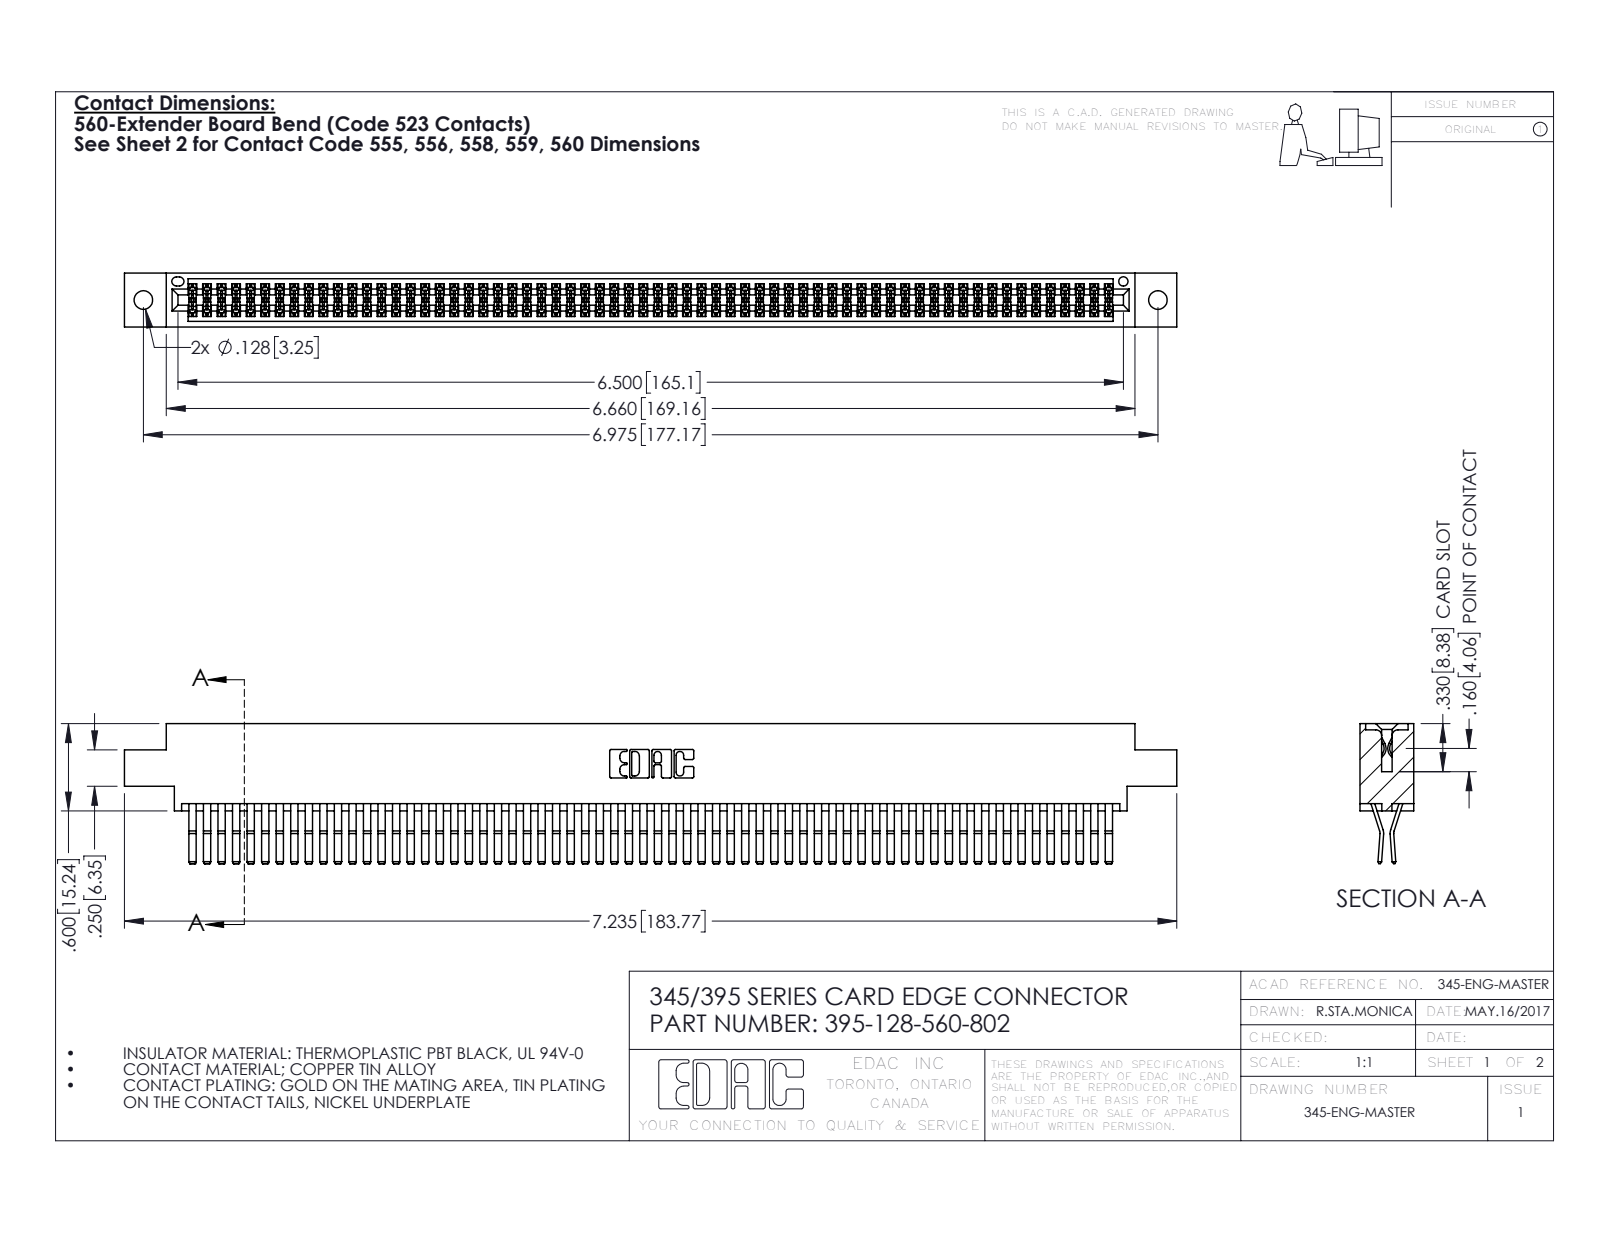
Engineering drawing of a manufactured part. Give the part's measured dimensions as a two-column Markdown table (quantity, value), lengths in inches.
| quantity | value |
| --- | --- |
| part name | 345 Part_0.170 Offset - 0.128 Dia; 345-292-001_560 Tail; 395-128-560-802 |
| STEP written by | SolidWorks 2016 (CONFIG_CONTROL_DESIGN) |
| units | inches |
| bodies | 129 solids, 6786 faces (4308 planar, 2478 cylindrical, 0 other) |
| overall size | 7.235 × 0.962 × 0.37 |
| volume | 1.144 in³ |
| surface area | 46.75 in² |
| round holes (diameter × count) | 0.128 × 2, 0.064 × 1 |
| partial cylindrical surfaces (radius × count) | 0.006 × 192, 0.01 × 22, 0.007 × 6, 0.031 × 6, 0.026 × 3, 0.01 × 2, 0.014 × 2, 0.019 × 2 |
| main face-to-face distances | 0.025, 0.298, 0.072, 0.37, 0.2, 0.098, 0.272, 0.225, 0.175, 0.149 |
| hole center spacings | 0.27, 6.739, 6.975 |
